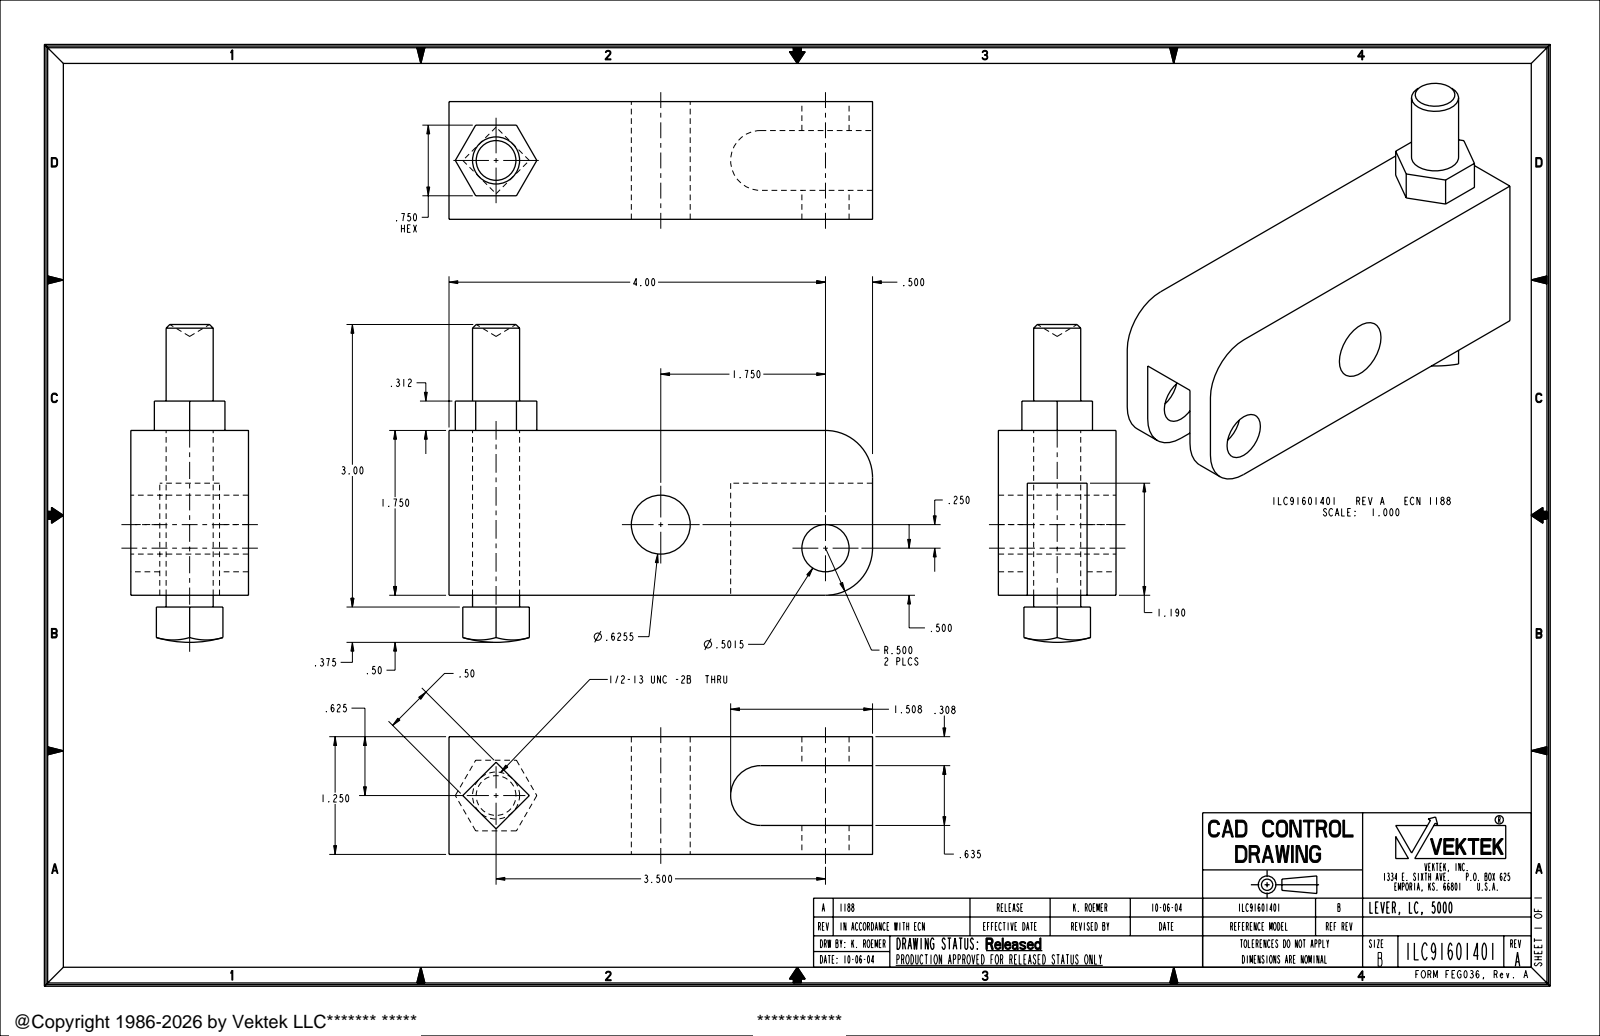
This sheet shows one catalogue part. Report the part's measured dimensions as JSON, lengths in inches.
{"part_name": "91601401", "step_written_by": "PRO/ENGINEER BY PARAMETRIC TECHNOLOGY CORPORATION, 2004290 (CONFIG_CONTROL_DESIGN)", "units": "inches", "bodies": {"solids": 1, "faces": 46, "planar": 24, "cylindrical": 16, "other": 6}, "overall_size": [4.5, 3.375, 1.25], "volume_in3": 8.569, "surface_area_in2": 41.75, "round_holes": [[0.501, 1], [0.626, 1]], "round_bosses_or_shafts": [[0.5, 1]], "partial_cylinders_radius": [[0.5, 2], [0.317, 1]], "face_to_face_distances": [1.25, 1.75, 0.308, 0.943, 0.635, 1.19, 0.56, 4.5, 0.5, 2.062], "hole_center_spacings": [1.768]}
